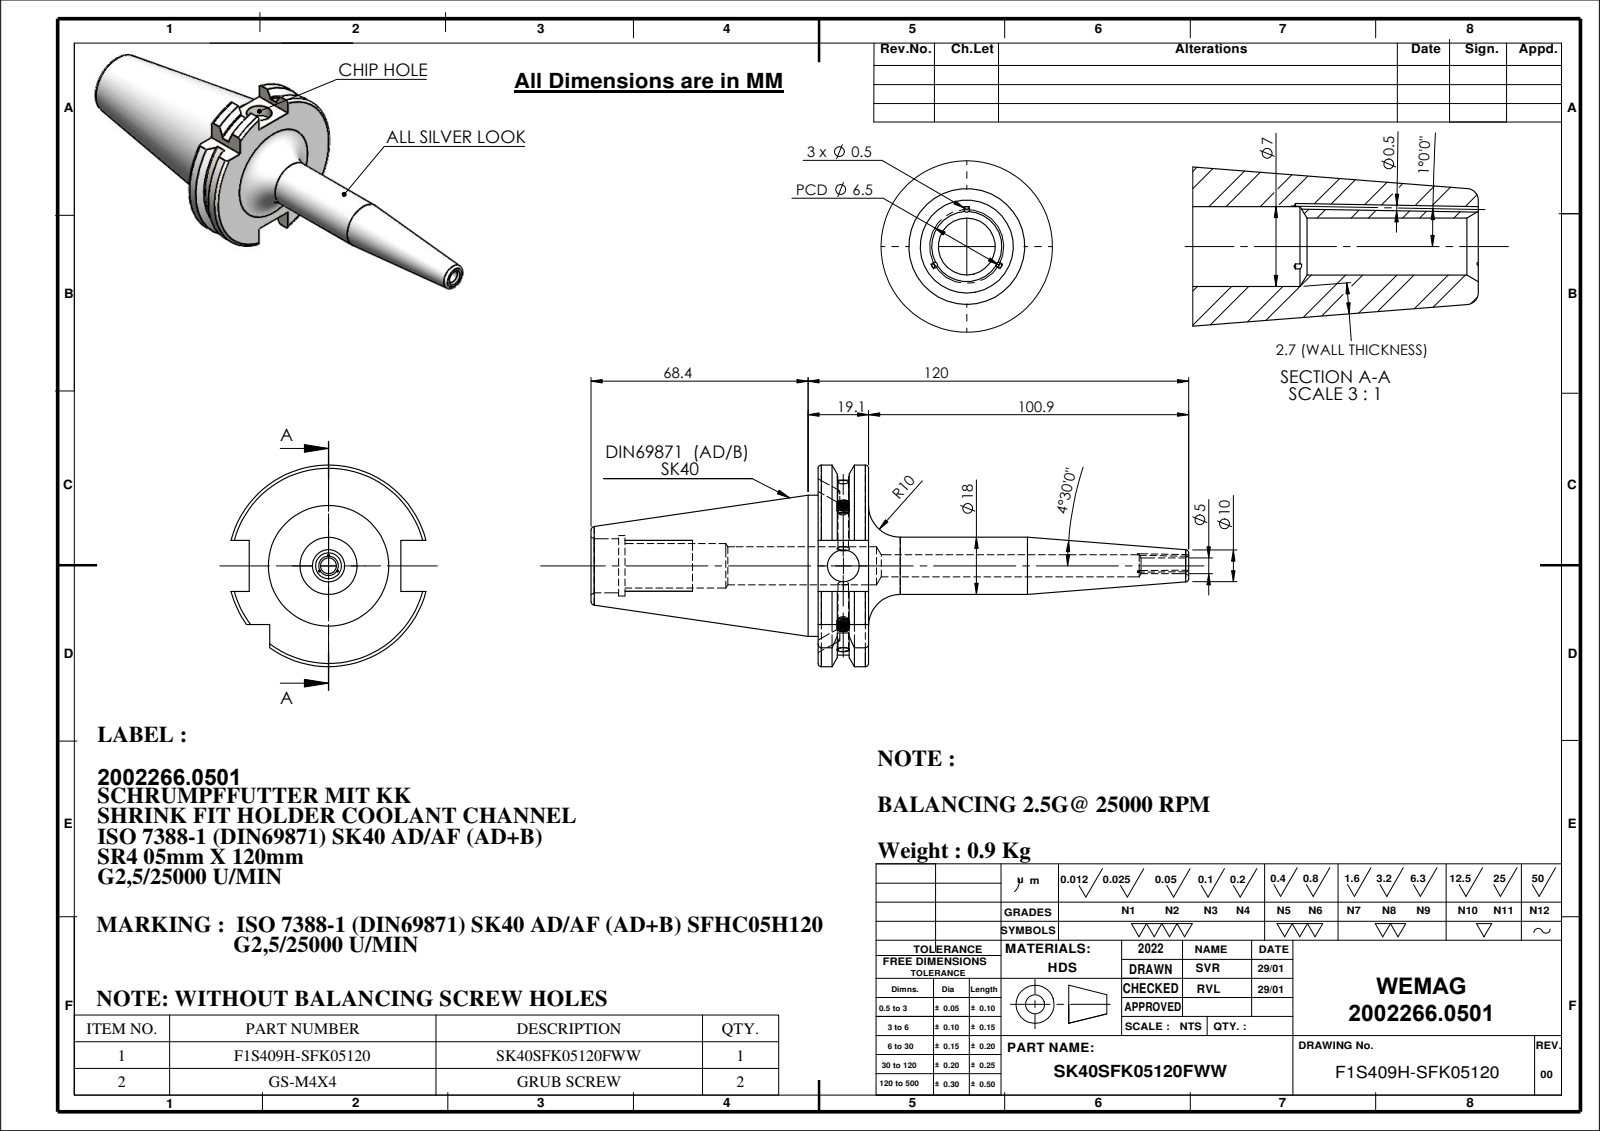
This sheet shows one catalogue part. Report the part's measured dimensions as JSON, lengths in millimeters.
{"part_name": "SK40SFK05120FWW; 91406-SR405120; GS-M4X4_DIN 913 - M4 x 4-N", "step_written_by": "SolidWorks 2018 (CONFIG_CONTROL_DESIGN)", "units": "millimeters", "bodies": {"solids": 3, "faces": 208, "planar": 46, "cylindrical": 60, "other": 102}, "overall_size": [188.4, 63.55, 61.48], "volume_mm3": 118624, "surface_area_mm2": 28336, "round_holes": [[0.5, 3], [3.3, 1], [4.99, 1], [7, 1], [10, 1], [12, 1], [14, 1], [17, 1], [19, 1]], "round_bosses_or_shafts": [[4, 2], [44.45, 1], [18, 1]], "partial_cylinders_radius": [[28.12, 1], [31.77, 1]], "face_to_face_distances": [15.9, 16.1, 47.8, 71.6, 87.5, 10.7, 60.9, 76.8, 77.62, 66.92]}
